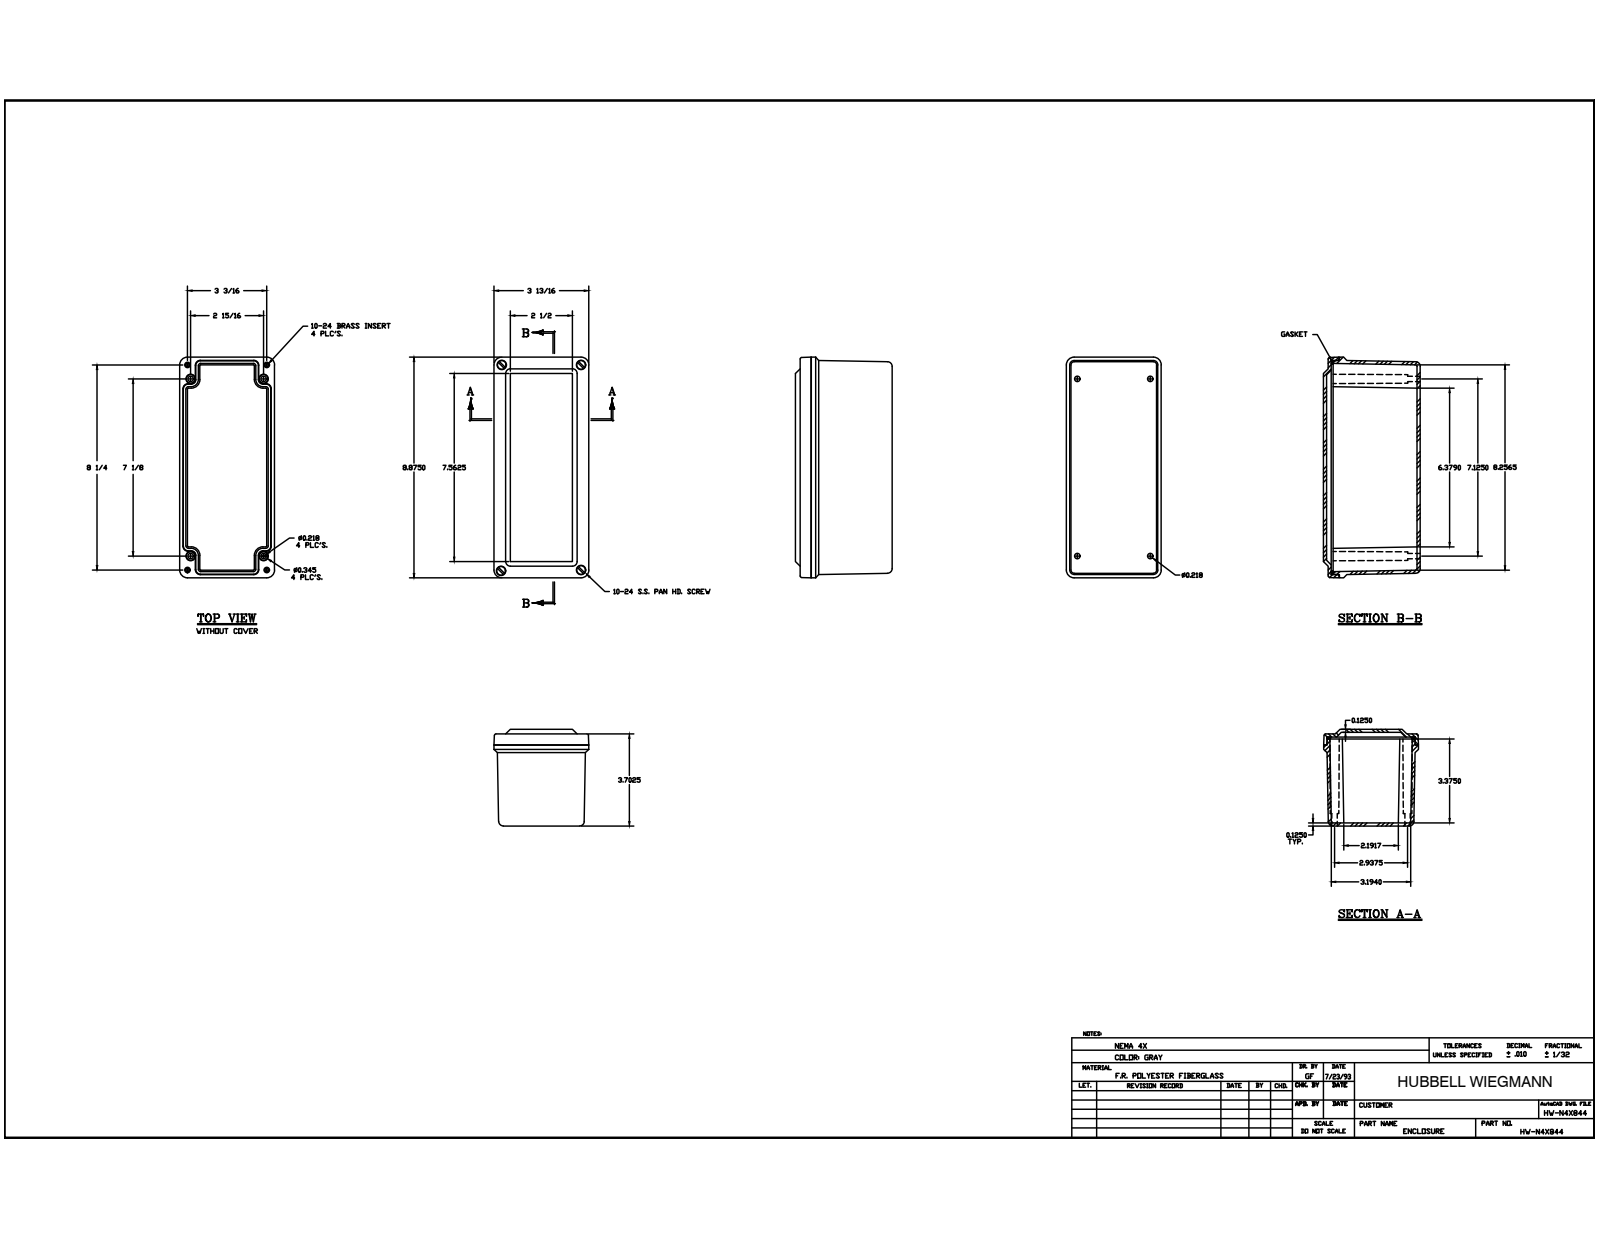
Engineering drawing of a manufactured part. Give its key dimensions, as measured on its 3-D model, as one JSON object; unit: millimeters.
{"part_name": "10-24 X 0.4375 DP BRASS INSERT; 10-24x0.75 DP combo screw; WPCF844 BOX; WPCF844 GASKET (+3 more)", "step_written_by": "Autodesk Inventor 2014 (AUTOMOTIVE_DESIGN)", "units": "millimeters", "bodies": {"solids": 11, "faces": 379, "planar": 183, "cylindrical": 100, "other": 96}, "overall_size": [225.43, 98.42, 96.84], "volume_mm3": 405094, "surface_area_mm2": 217480, "round_holes": [[5.56, 8], [3.68, 4], [4.83, 4], [9.52, 4]], "round_bosses_or_shafts": [[9.42, 4], [5.54, 4], [4.5, 4]], "partial_cylinders_radius": [[0.79, 20], [0.3, 16], [1.59, 4], [4.47, 4], [4.76, 4], [5.59, 4], [7.94, 4], [8.26, 4]], "face_to_face_distances": [3.17, 3.34, 95.25, 4.76, 90.49, 98.42, 92.08, 12.7, 1.59, 87.32], "hole_center_spacings": [14.63, 79.09, 195.29, 210.19, 74.62, 80.96, 180.98, 195.76]}
